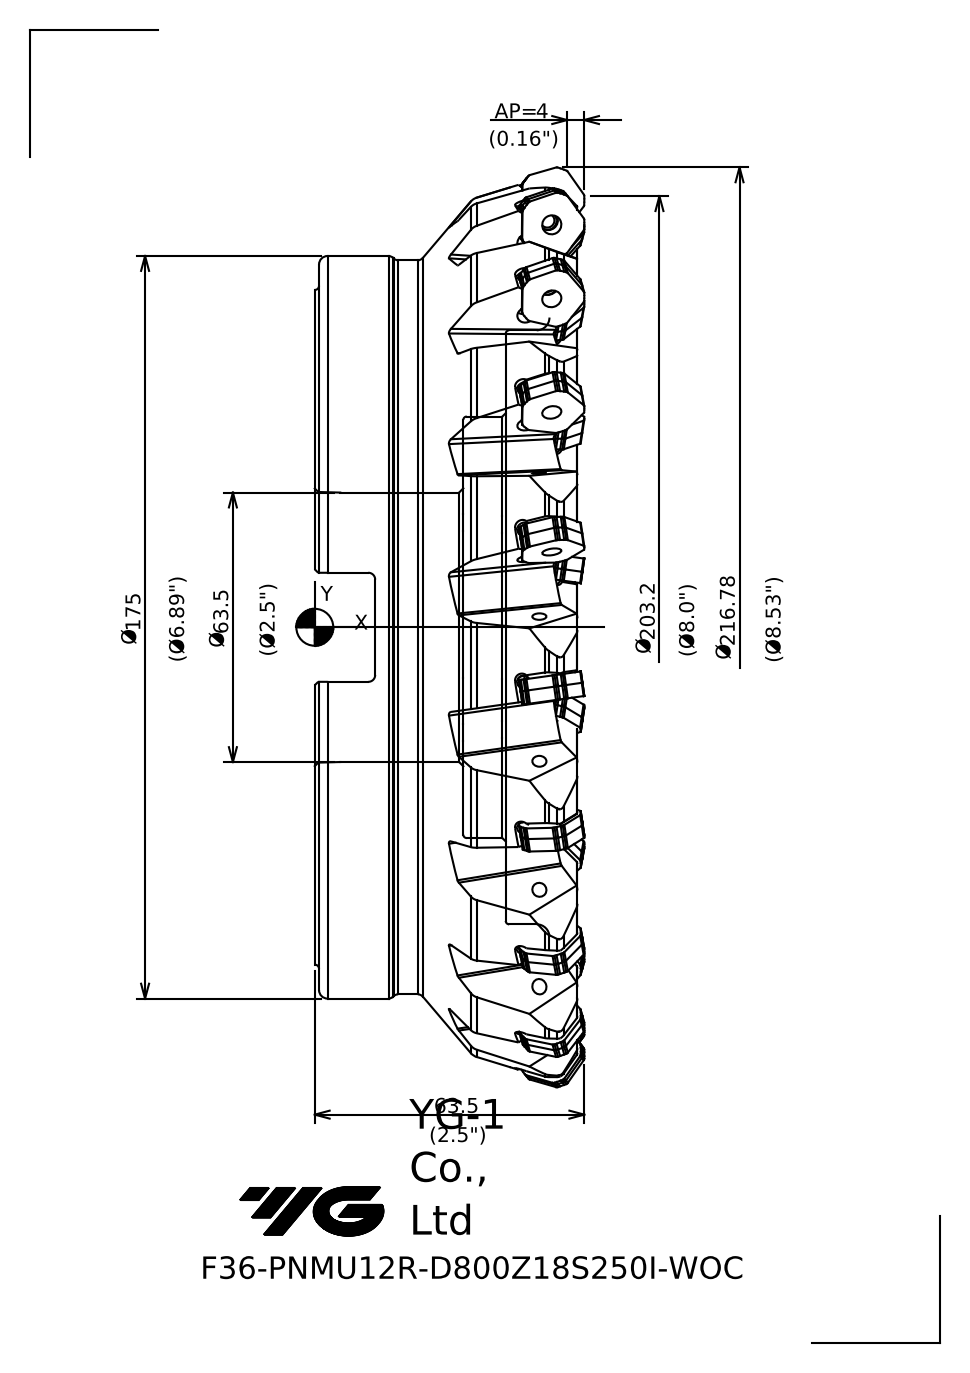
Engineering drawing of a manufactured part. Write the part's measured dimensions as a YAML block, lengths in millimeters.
part_name: "10221A6C8B27vrcz"
step_written_by: "SIEMENS PLM Software NX 10.0 (AP203_CONFIGURATION_CONTROLLED_3D_DESIGN_OF_MECHANICAL_PARTS_AND_ASSEMBLIES_MIM_LF)"
units: millimeters
bodies: {solids: 1, faces: 167, planar: 33, cylindrical: 37, other: 97}
overall_size: [216.73, 216.73, 63.54]
volume: 1151000
surface_area: 145338
round_holes:
  - {diameter: 18, count: 4}
  - {diameter: 63.5, count: 1}
  - {diameter: 140, count: 1}
round_bosses_or_shafts:
  - {diameter: 212.6, count: 1}
  - {diameter: 175, count: 1}
  - {diameter: 173, count: 1}
partial_cylinders:
  - {radius: 10, count: 8}
  - {radius: 0.8, count: 4}
  - {radius: 13.75, count: 4}
  - {radius: 1.6, count: 2}
  - {radius: 41, count: 1}
face_to_face_distances: [45, 10, 35, 30.78, 20.78, 14.22, 44, 34, 13.22, 1]
hole_center_spacings: [50.8, 71.84, 101.6]
